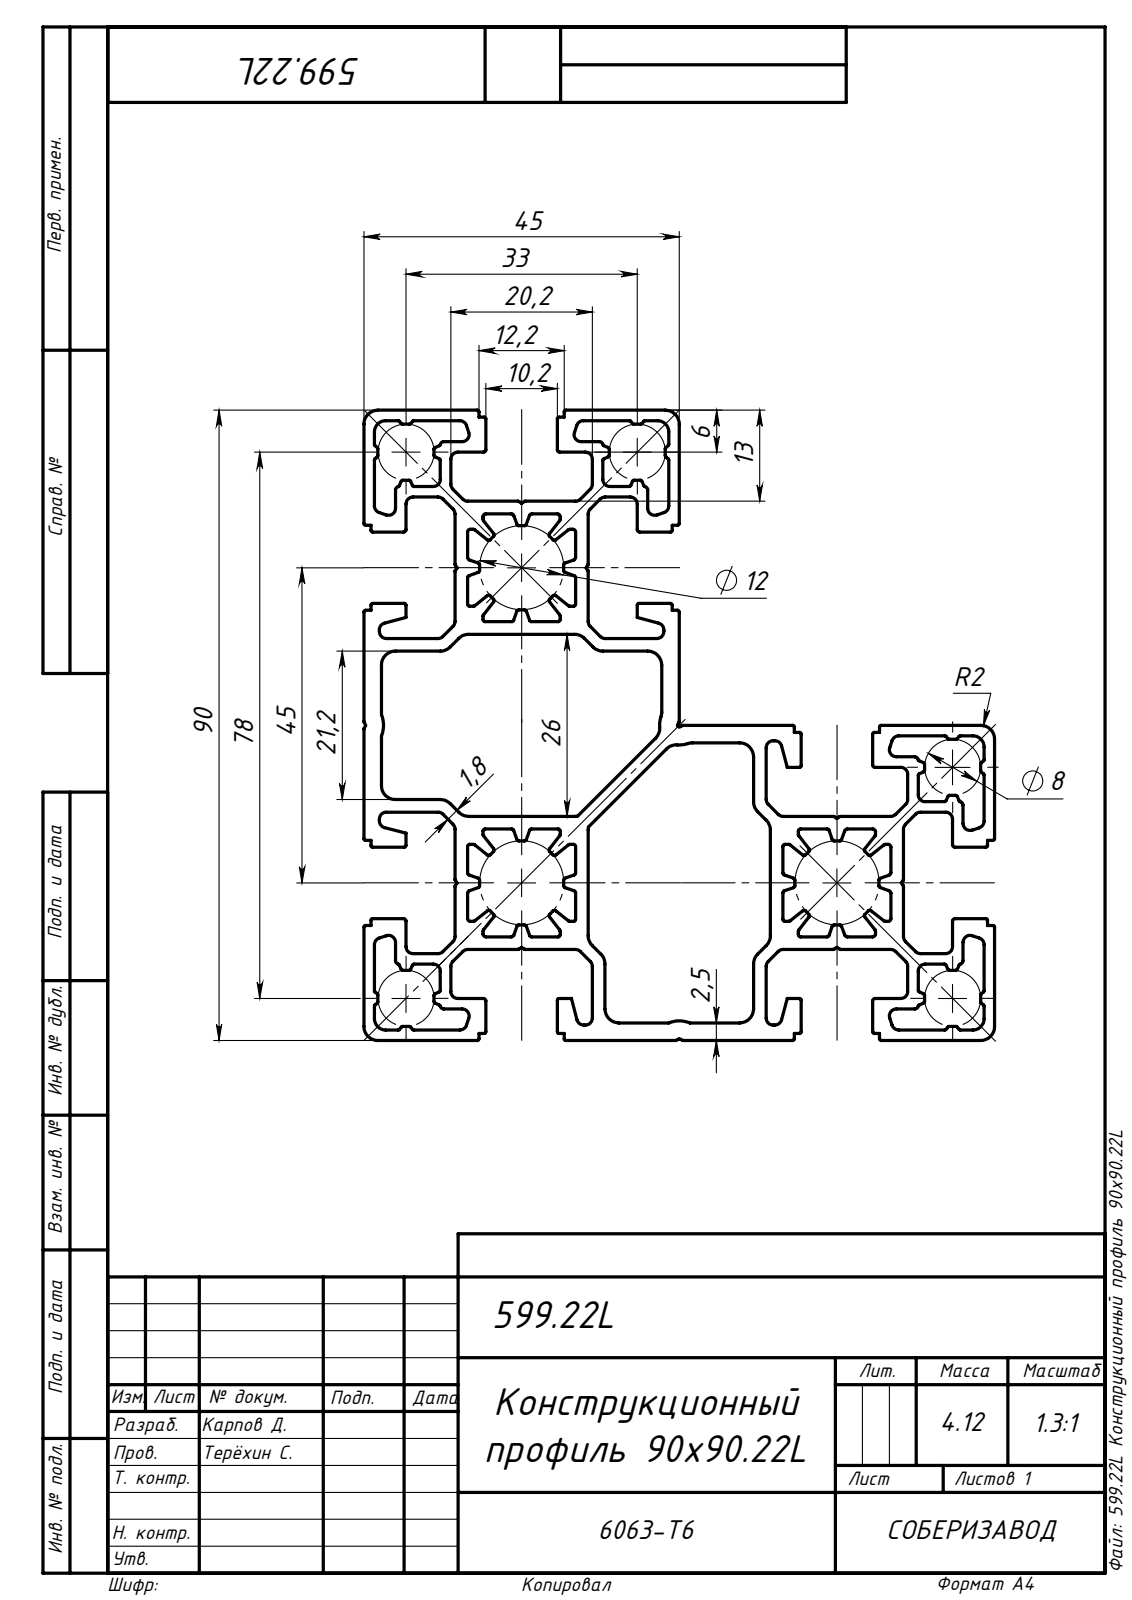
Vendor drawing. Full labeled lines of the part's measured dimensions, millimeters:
STEP written by: SolidWorks 2019 (AUTOMOTIVE_DESIGN)
Units: millimetres
Bodies: 1 solid, 832 faces (421 planar, 411 cylindrical, 0 other)
Overall size (bounding box): 1000 × 90 × 90
Volume: 1 528 000 mm³ · Surface area: 1 489 000 mm²
Partial cylindrical surfaces — rounded edges, fillets, slot ends (radius × count): R0.25 ×163, R1 ×79, R0.3 ×70, R0.4 ×30, R2 ×29, R0.35 ×10, R0.5 ×10, R1.6 ×5
Main face-to-face distances: 45, 13, 32, 1.8, 58, 19, 77, 25.4, 17.4, 4.4
